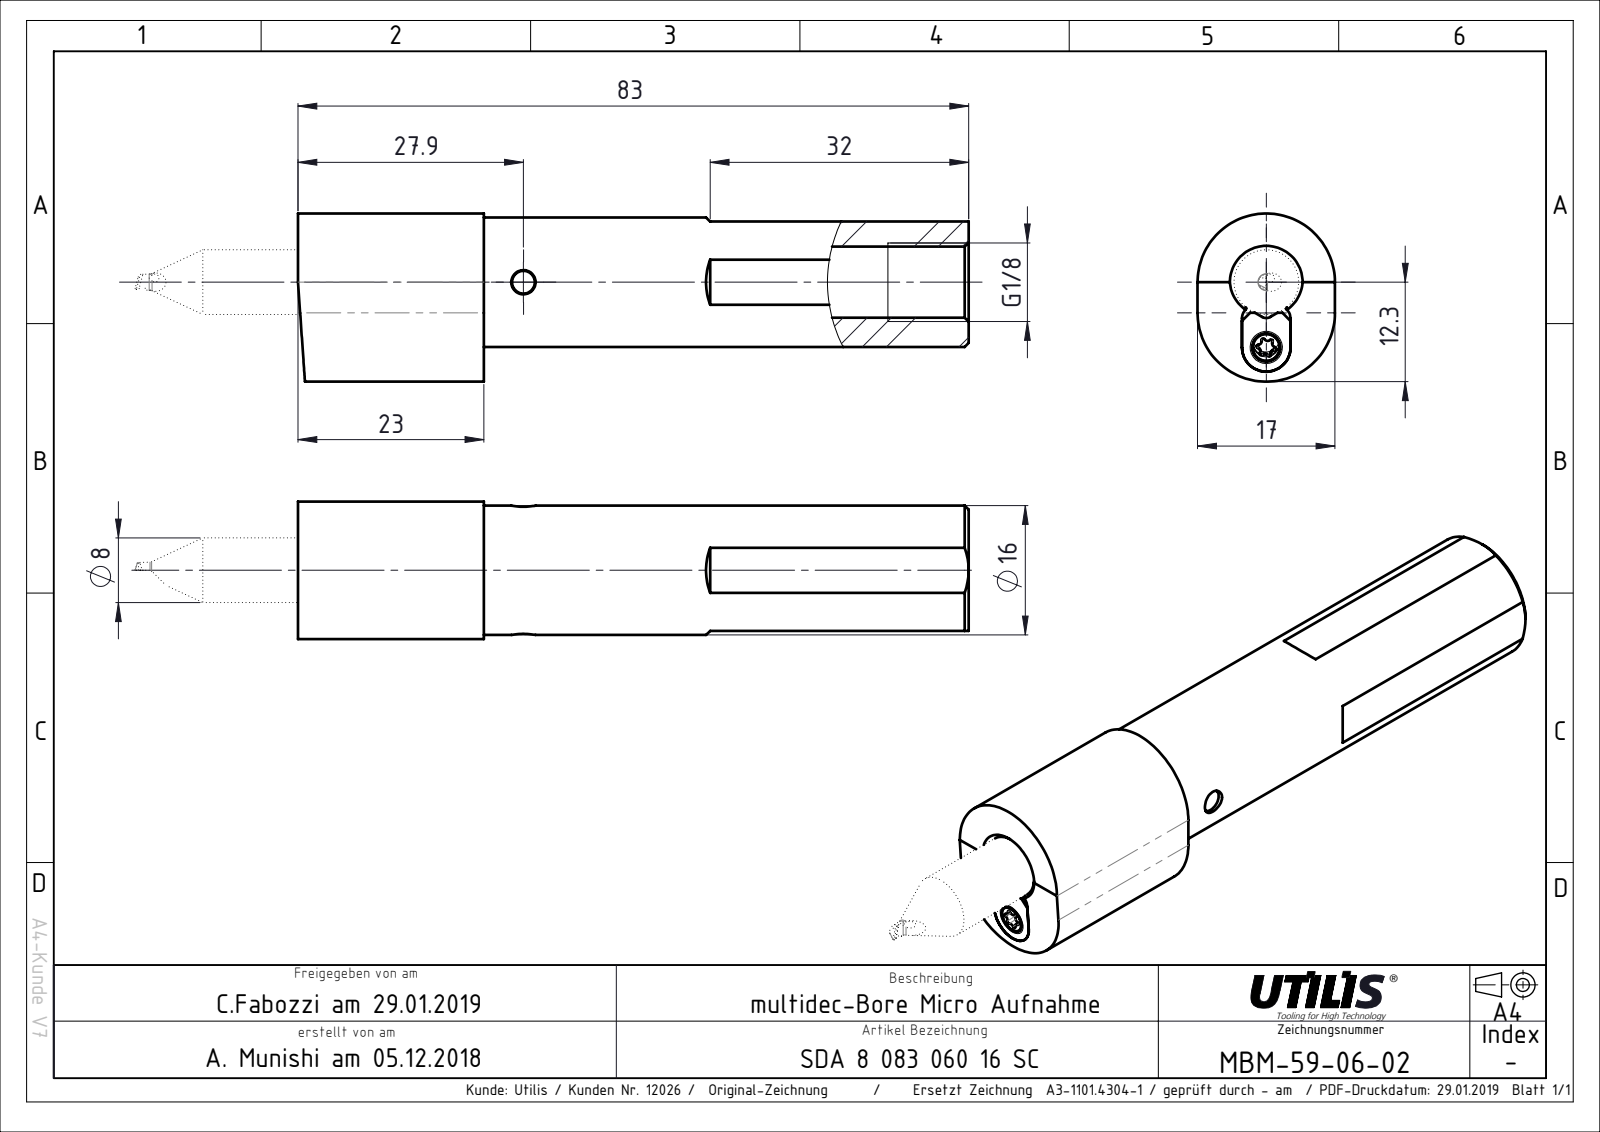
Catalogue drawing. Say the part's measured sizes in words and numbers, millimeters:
The part is named "MBM-59-06-02". Its 3-D file was written by "SolidWorks 2018 (CONFIG_CONTROL_DESIGN)". It is 1 solid with 45 faces: 13 planar, 16 cylindrical and 16 other. Overall it measures 83 by 20.8 by 17 millimeters. Its volume is 13 314 cubic millimeters and its surface area 7 335 square millimeters. Round holes: 1 of diameter 3, 1 of diameter 3.3, 1 of diameter 8, 1 of diameter 8.8. Round bosses or shafts: 1 of diameter 16. Partial cylindrical surfaces (rounded edges, fillets, slot ends): 2 of radius 8.5, 1 of radius 3. The main face-to-face distances are 60, 1, 16, 17, 23, 83, 5.5, 11.5, 4.5, 6.
